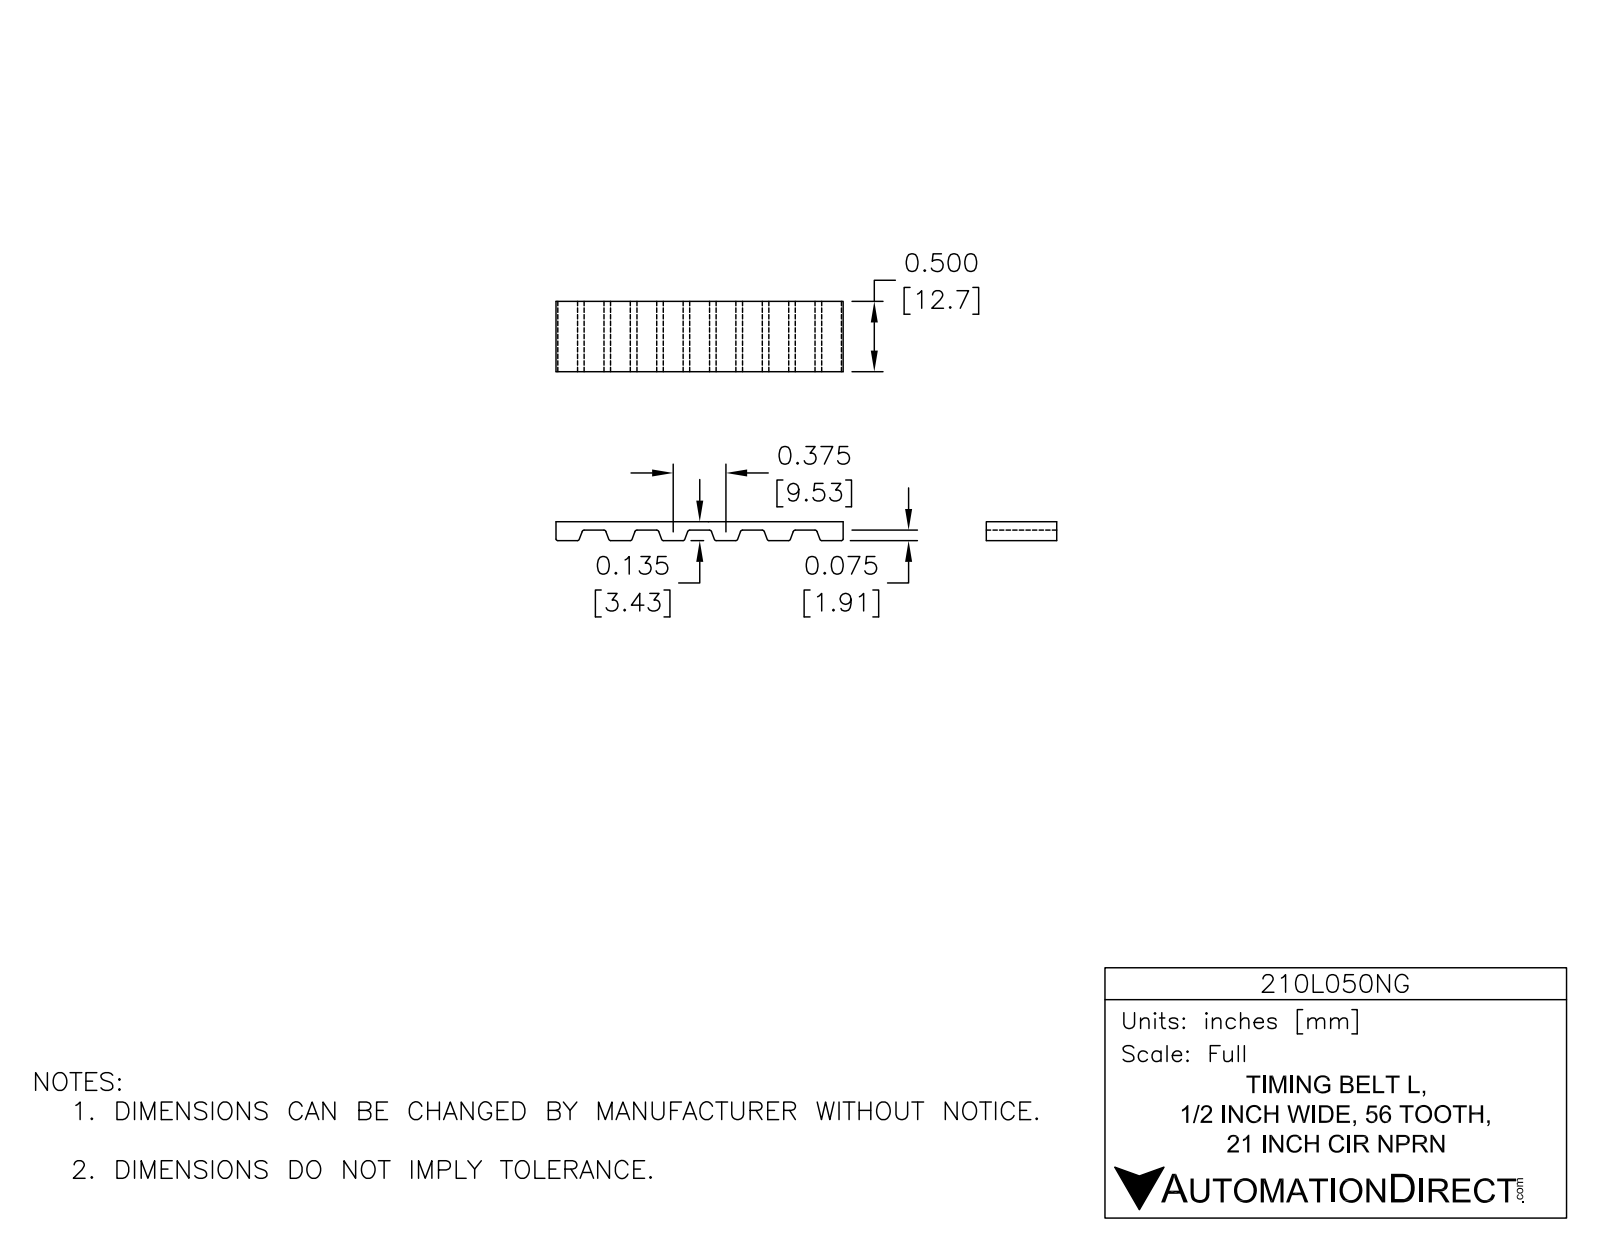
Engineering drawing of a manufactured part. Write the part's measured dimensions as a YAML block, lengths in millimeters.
part_name: "210L050NG"
step_written_by: "SolidWorks 2014 (AUTOMOTIVE_DESIGN)"
units: millimeters
bodies: {solids: 1, faces: 462, planar: 200, cylindrical: 262, other: 0}
overall_size: [223.2, 76.2, 12.7]
volume: 15500
surface_area: 17460
partial_cylinders:
  - {radius: 0.5, count: 220}
  - {radius: 36.4, count: 2}
  - {radius: 38.1, count: 2}
face_to_face_distances: [1.7, 74.5, 76.2, 12.7, 72.9, 3.6, 72.6, 1.9, 71, 26.8]
